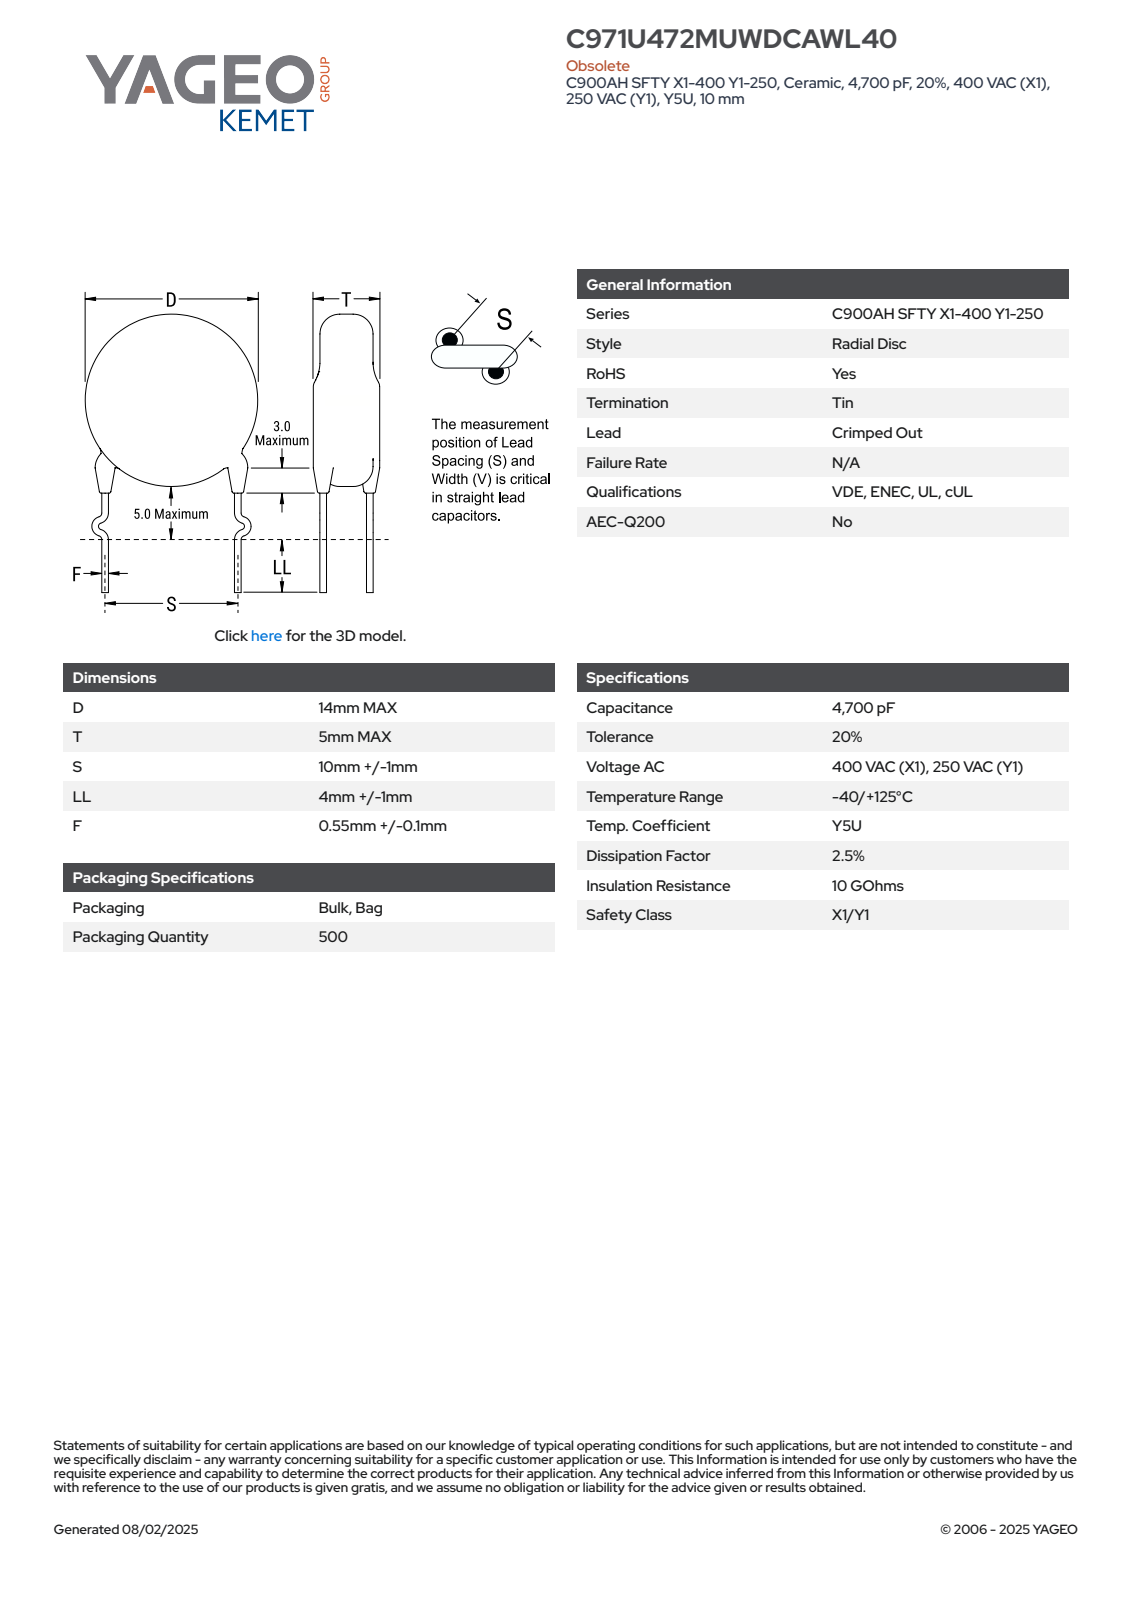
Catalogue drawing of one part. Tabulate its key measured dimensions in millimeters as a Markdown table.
| quantity | value |
| --- | --- |
| part name | CCD_KCOC900_D14T5S10LL5F0.55 |
| STEP written by | SolidWorks 2014 (AUTOMOTIVE_DESIGN) |
| units | millimeters |
| bodies | 4 solids, 85 faces (63 planar, 6 cylindrical, 16 other) |
| overall size | 24 × 15.15 × 5 |
| volume | 764 mm³ |
| surface area | 567 mm² |
| round bosses / shafts (diameter × count) | 1.2 × 2, 14 × 1 |
| main face-to-face distances | 5, 7.74, 6.29, 1.45, 0.4, 5.94, 0.9, 1.17, 4.31, 4.48 |
